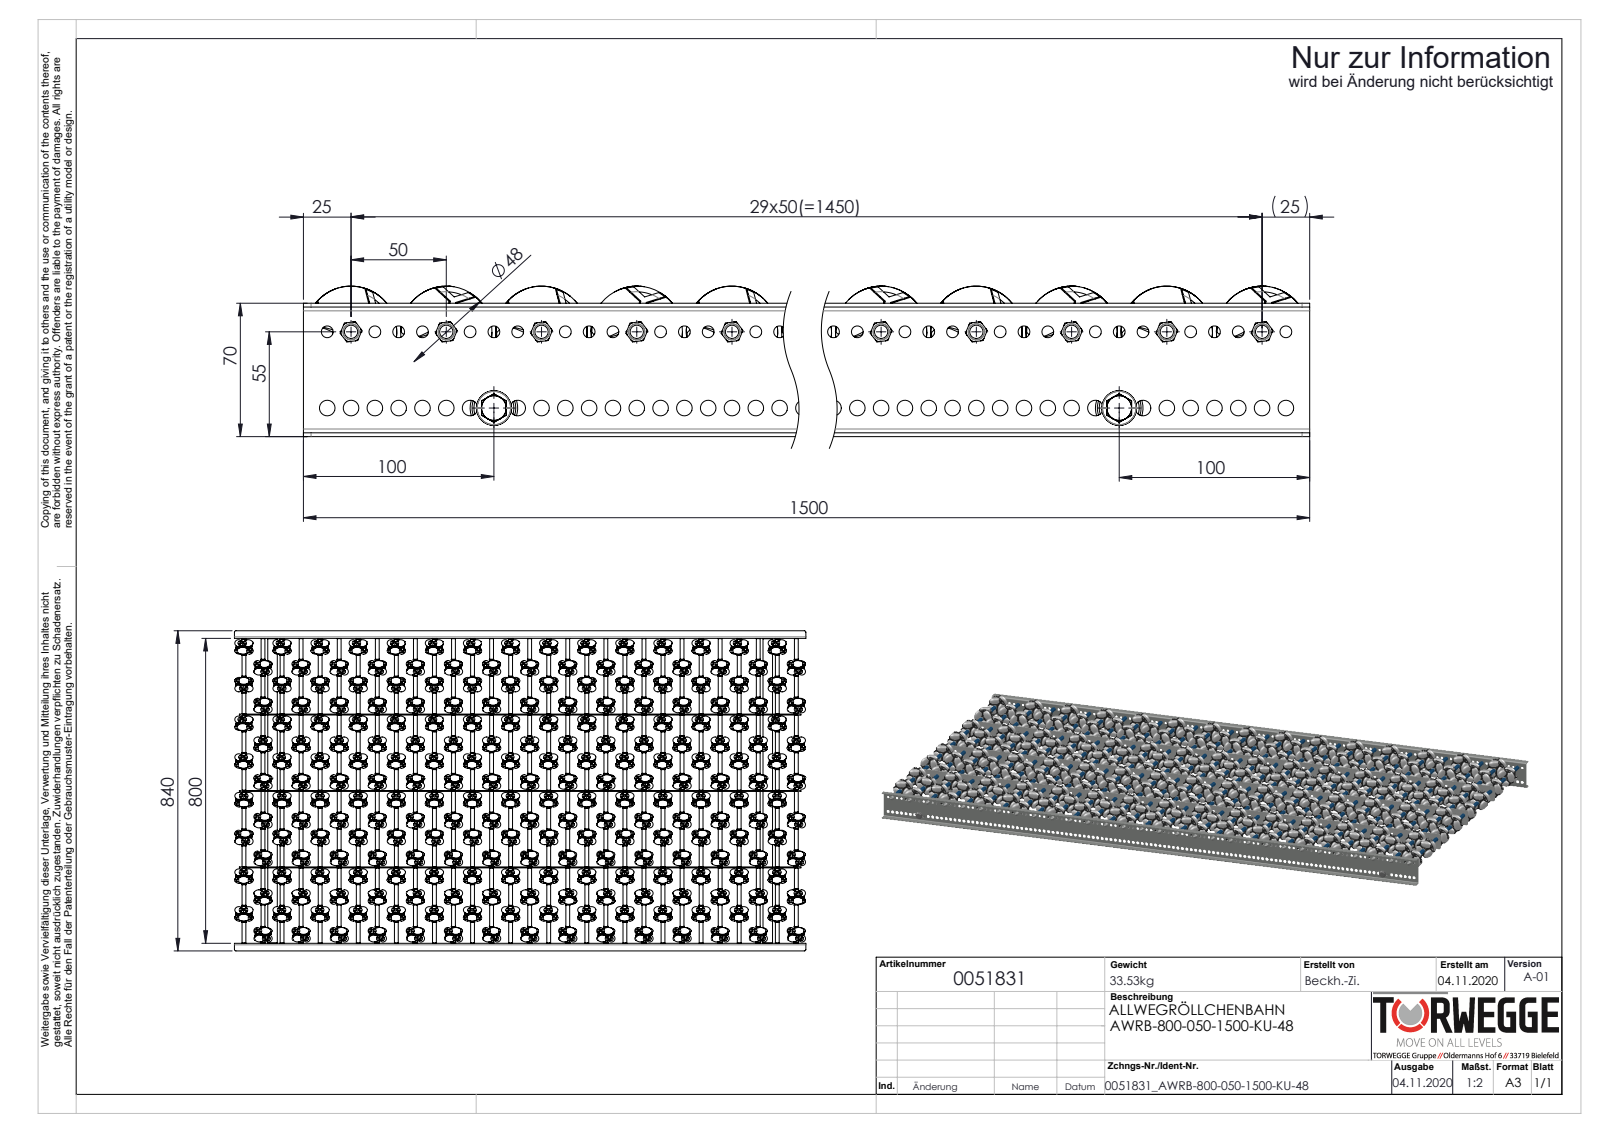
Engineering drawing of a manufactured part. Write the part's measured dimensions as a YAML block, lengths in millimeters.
part_name: "0015028_AWR48; 0027528_BUCHSE-HOHLNIETE ZU AWR48; 0019719_Gewindestange-M6_L=820; AWR48_Halter (+8 more)"
step_written_by: "SolidWorks 2020 (AUTOMOTIVE_DESIGN)"
units: millimeters
bodies: {solids: 3945, faces: 68876, planar: 21261, cylindrical: 23751, other: 23864}
overall_size: [1500, 840, 79]
volume: 12780000
surface_area: 8483000
round_holes:
  - {diameter: 3.7, count: 1290}
  - {diameter: 4.2, count: 1290}
  - {diameter: 6.2, count: 119}
  - {diameter: 8.2, count: 119}
  - {diameter: 6.5, count: 59}
  - {diameter: 8.4, count: 27}
  - {diameter: 6.8, count: 2}
  - {diameter: 21, count: 2}
round_bosses_or_shafts:
  - {diameter: 4, count: 1290}
  - {diameter: 3.7, count: 1151}
  - {diameter: 8, count: 28}
  - {diameter: 47.1, count: 27}
  - {diameter: 42, count: 27}
  - {diameter: 11, count: 27}
  - {diameter: 10, count: 27}
  - {diameter: 6, count: 27}
partial_cylinders:
  - {radius: 4, count: 8}
  - {radius: 1.85, count: 6}
  - {radius: 2, count: 4}
  - {radius: 5, count: 4}
face_to_face_distances: [2, 200.5, 2.5, 802, 401, 198, 203, 68, 800, 804]
hole_center_spacings: [36.05, 36.06, 99, 36.07, 122.72, 36.04, 121.92, 71.16]
